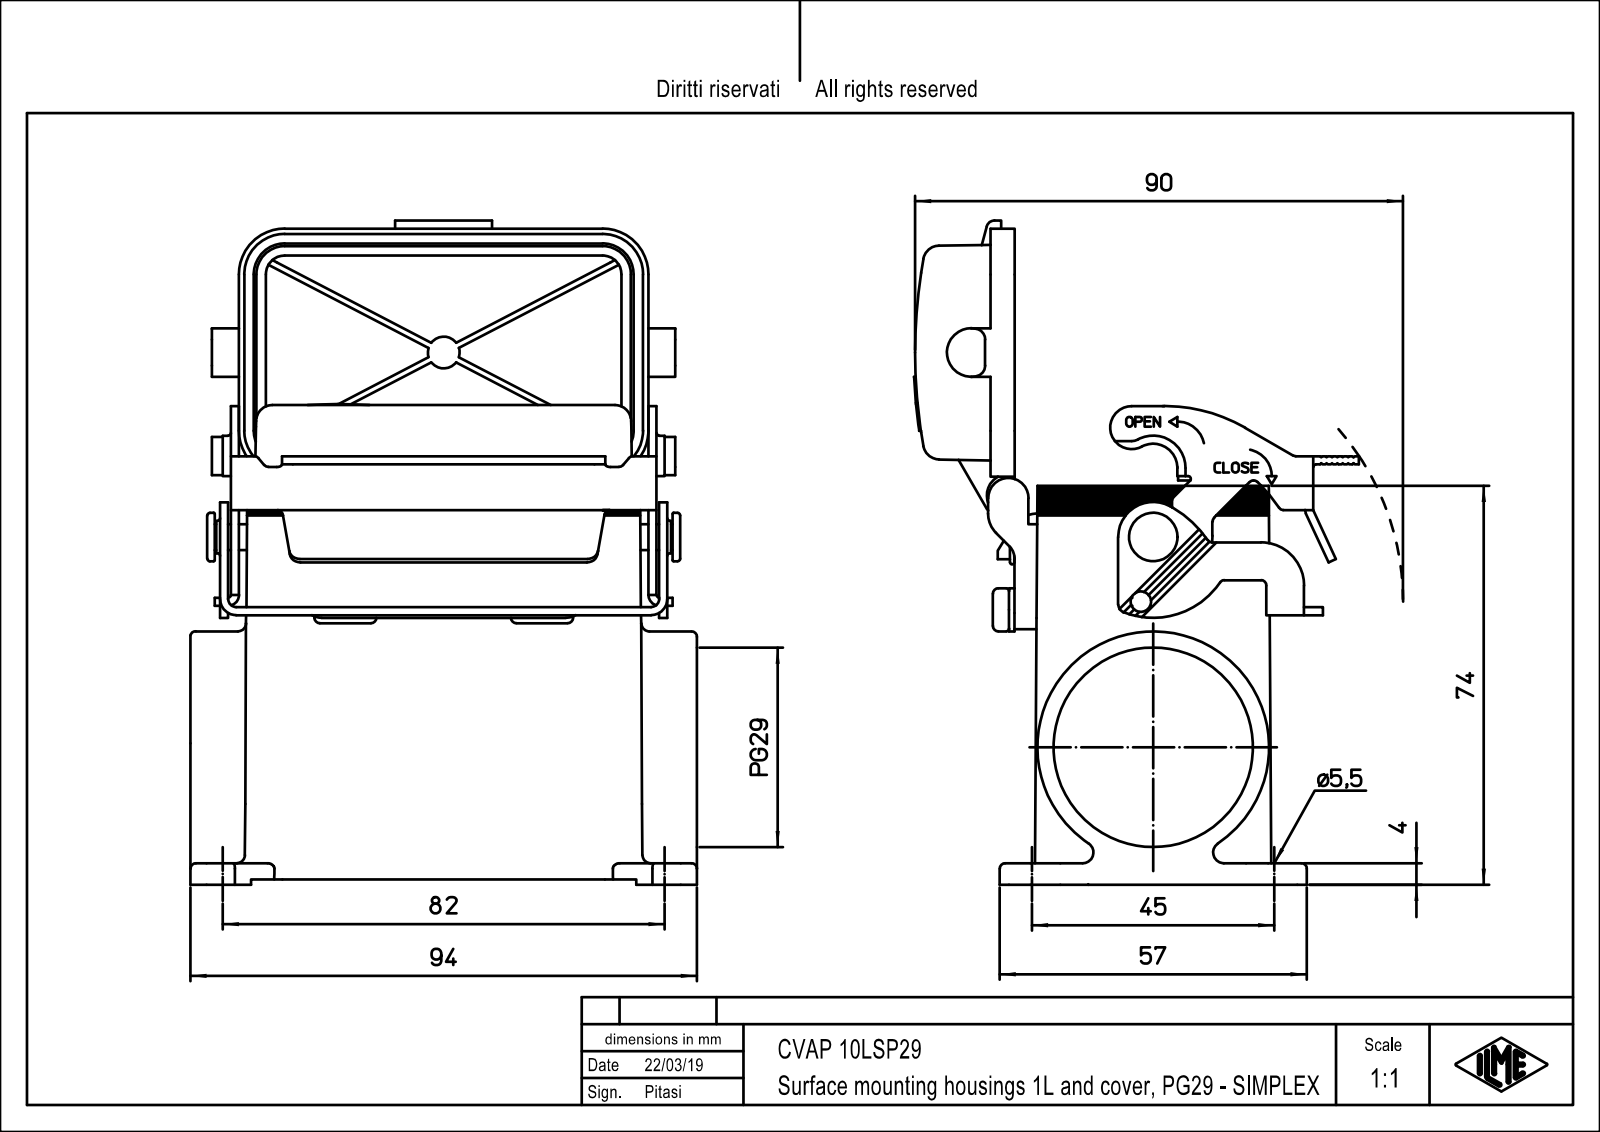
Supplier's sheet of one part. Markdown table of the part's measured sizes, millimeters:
| quantity | value |
| --- | --- |
| part name | CVAP_10LSP29 |
| STEP written by | PTC Creo Elements/Direct Modeling 19.0E 27-Jun-2016 (C) Parametric Technology GmbH (AUTOMOTIVE_DESIGN) |
| units | millimeters |
| bodies | 1 solid, 617 faces (384 planar, 209 cylindrical, 24 other) |
| overall size | 122.72 × 93.5 × 79.7 |
| volume | 113 964 mm³ |
| surface area | 70 871 mm² |
| round holes (diameter × count) | 2.46 × 4, 3 × 4, 5.5 × 4, 32 × 1, 37 × 1 |
| round bosses / shafts (diameter × count) | 0.8 × 3, 43 × 1, 9 × 1, 8.4 × 1, 8 × 1, 6 × 1, 4 × 1, 2.4 × 1 |
| partial cylindrical surfaces (radius × count) | 2 × 22, 3 × 13, 1.5 × 8, 3.5 × 7, 1 × 5, 6 × 5, 0.5 × 4, 1.8 × 4 |
| main face-to-face distances | 4, 40.5, 2, 36.5, 1.5, 44.5, 71.75, 4.25, 6.25, 6 |
| hole center spacings | 15.4, 38.11, 70.08, 78.27, 27, 45, 57, 63.07 |
